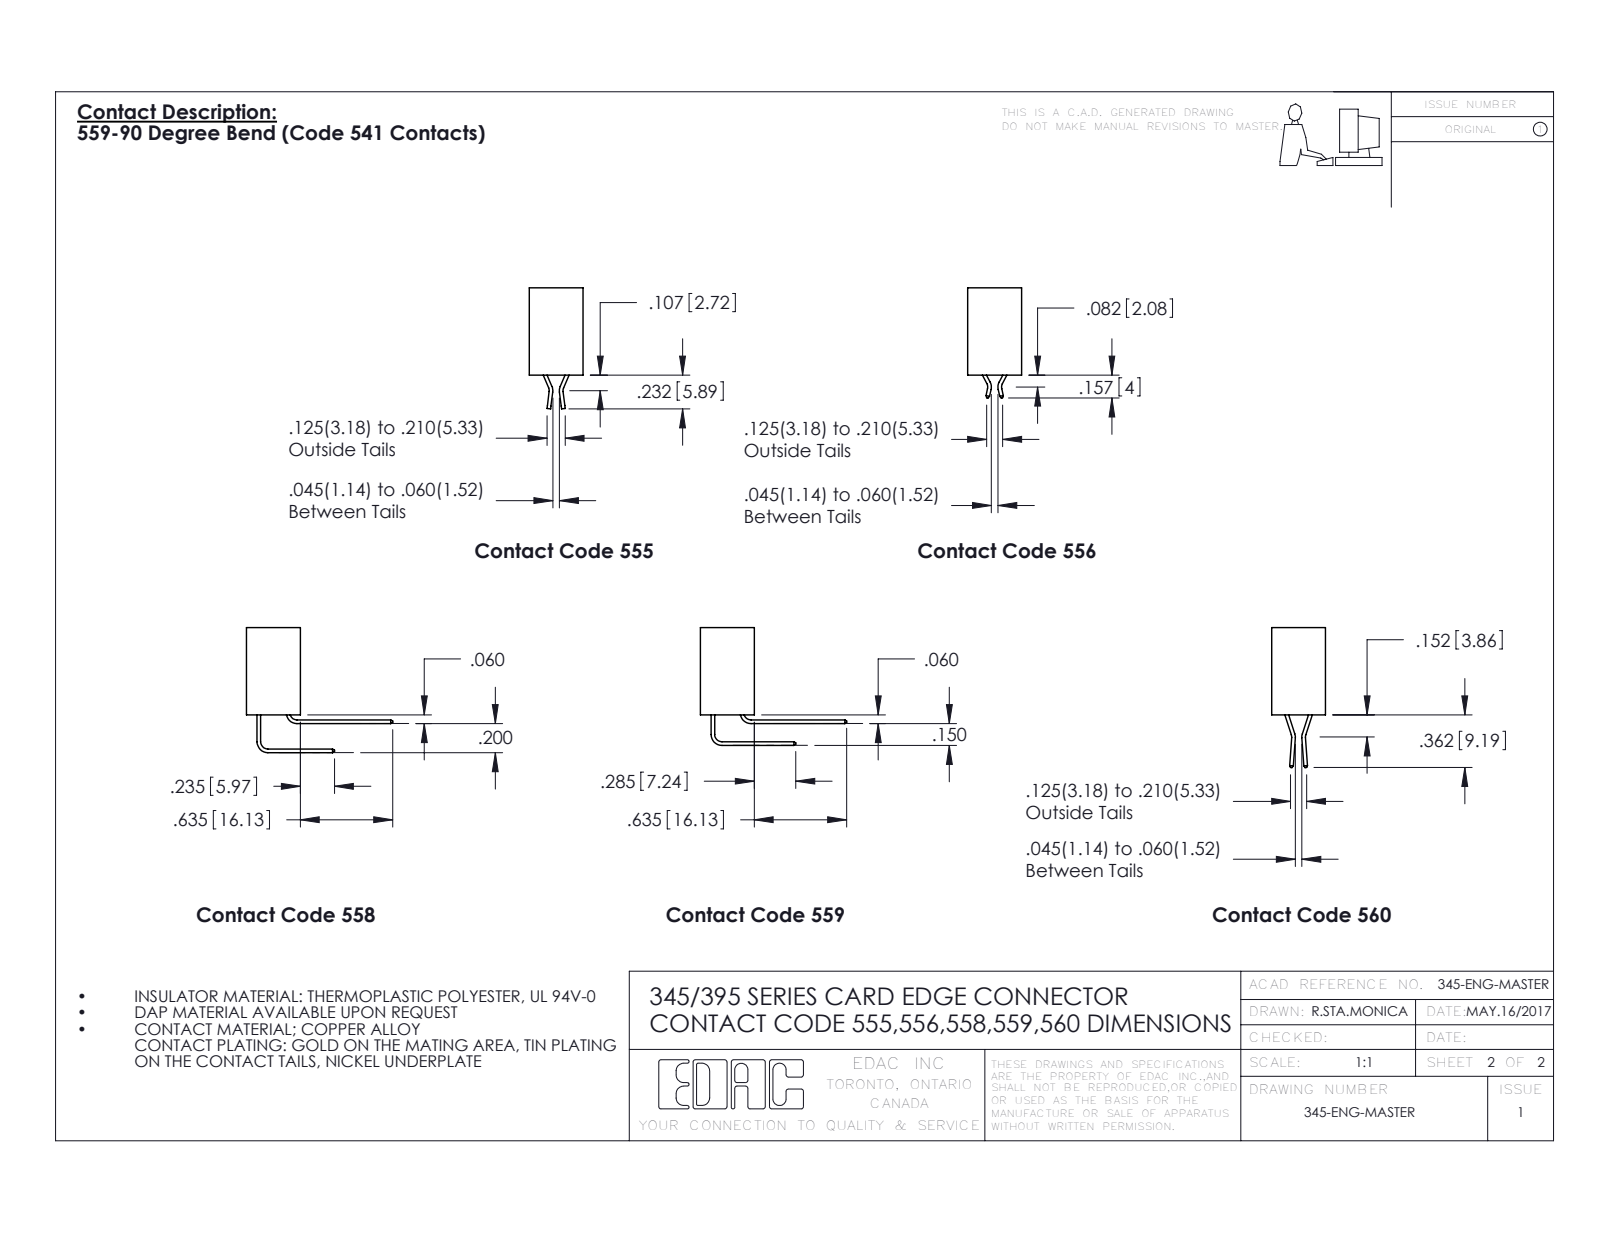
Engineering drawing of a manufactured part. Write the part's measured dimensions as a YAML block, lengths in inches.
part_name: "345 Part_Flush Mounting Lugs - Side Mount; 345-292-001_558 559 Tail - 1; 395-048-559-112"
step_written_by: "SolidWorks 2016 (CONFIG_CONTROL_DESIGN)"
units: inches
bodies: {solids: 49, faces: 3006, planar: 2096, cylindrical: 910, other: 0}
overall_size: [5.635, 1.005, 0.659]
volume: 0.837
surface_area: 29.62
round_holes:
  - {diameter: 0.128, count: 2}
  - {diameter: 0.064, count: 1}
partial_cylinders:
  - {radius: 0.006, count: 96}
  - {radius: 0.01, count: 22}
  - {radius: 0.007, count: 6}
  - {radius: 0.031, count: 6}
  - {radius: 0.026, count: 3}
  - {radius: 0.031, count: 2}
  - {radius: 0.04, count: 2}
  - {radius: 0.014, count: 1}
face_to_face_distances: [0.298, 0.072, 0.37, 0.2, 0.098, 0.272, 0.025, 0.225, 0.149, 0.072]
hole_center_spacings: [5.375]
